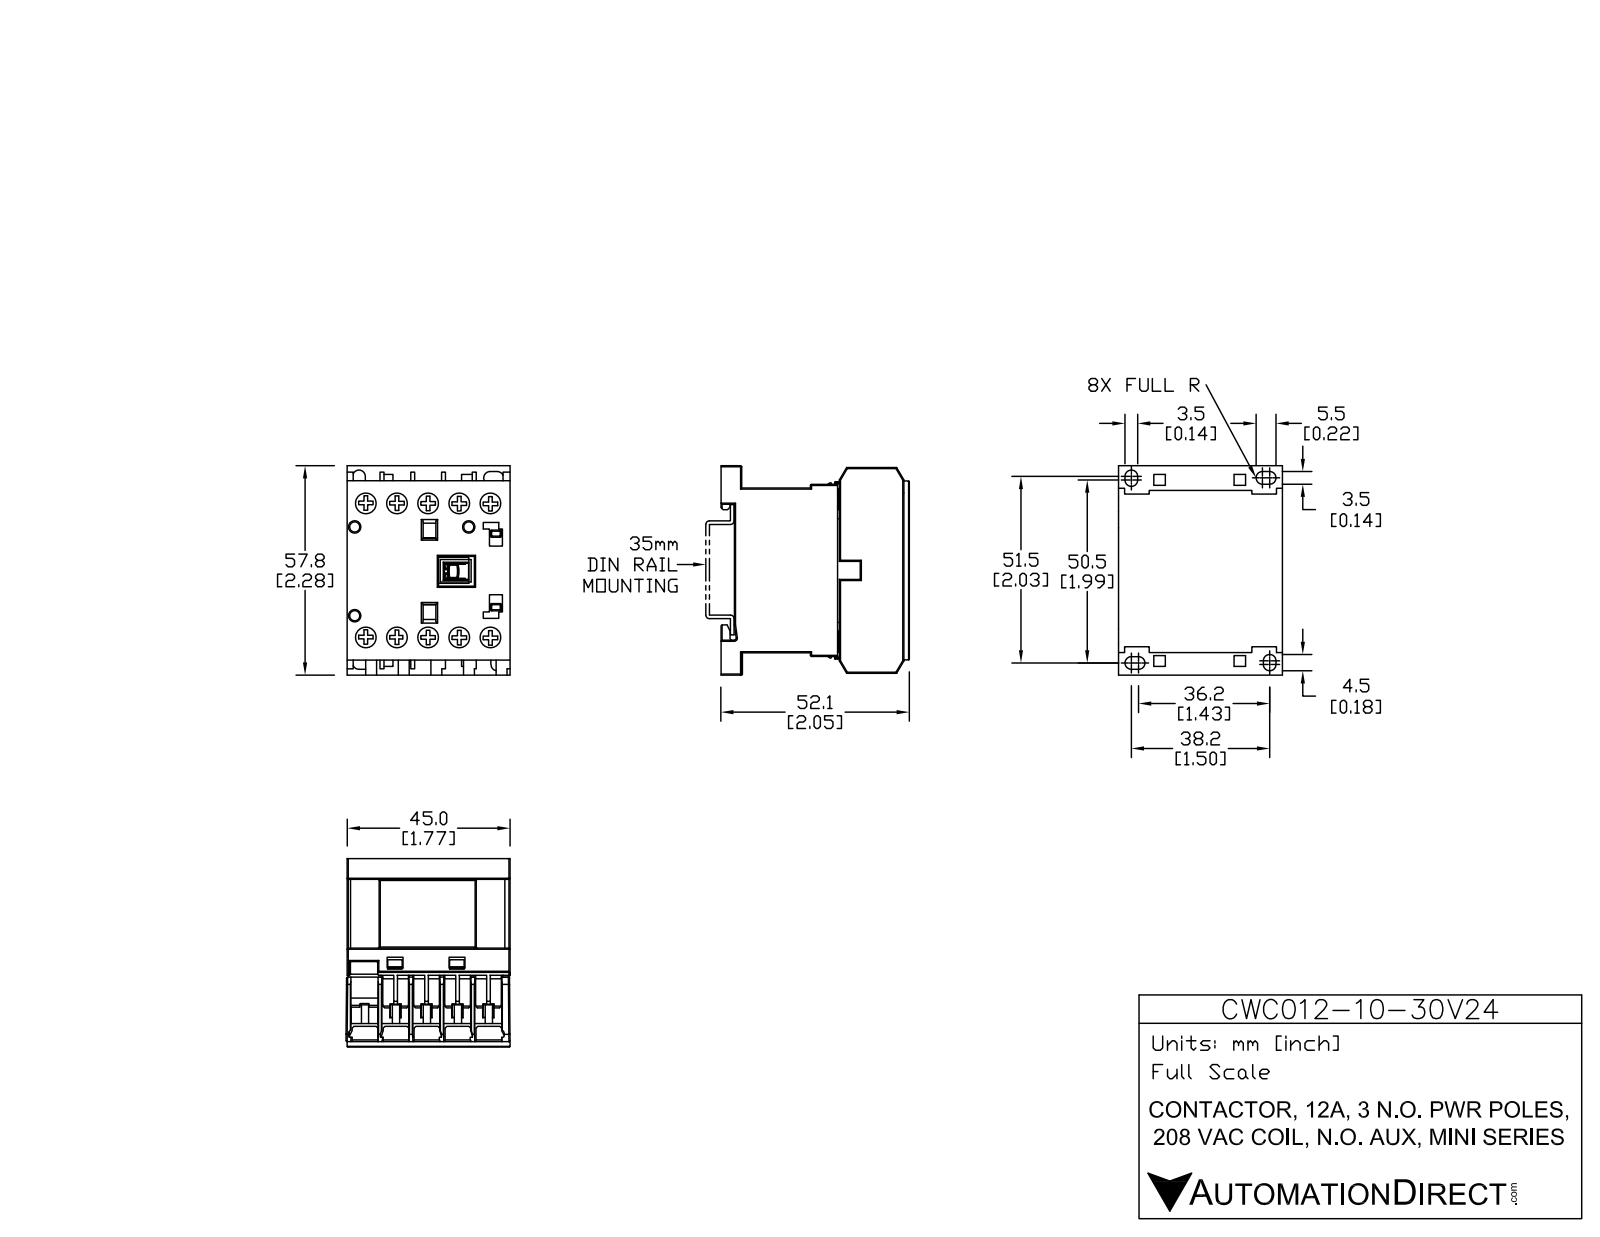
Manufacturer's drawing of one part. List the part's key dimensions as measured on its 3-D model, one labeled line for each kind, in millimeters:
Part name (STEP PRODUCT): CWC12-10-30V24
STEP written by: SolidWorks 2013 (AUTOMOTIVE_DESIGN)
Units: millimetres
Bodies: 15 solids, 535 faces (445 planar, 90 cylindrical, 0 other)
Overall size (bounding box): 58.04 × 52.12 × 45.75
Volume: 97 133 mm³ · Surface area: 30 437 mm²
Round holes (diameter × count): ⌀6.2 ×10, ⌀2.8 ×3
Round bosses / shafts (diameter × count): ⌀5.9 ×10
Partial cylindrical surfaces — rounded edges, fillets, slot ends (radius × count): R0.3 ×20, R1.72 ×6, R1.73 ×2, R0.32 ×1, R0.42 ×1, R0.55 ×1
Main face-to-face distances: 8.25, 45.5, 1.25, 16.5, 9.5, 5.5, 17.75, 5.13, 10.63, 7
Hole centre spacings: 8.55, 37.94, 17.1, 40.72, 36.96, 25.65, 44.99, 6.91
